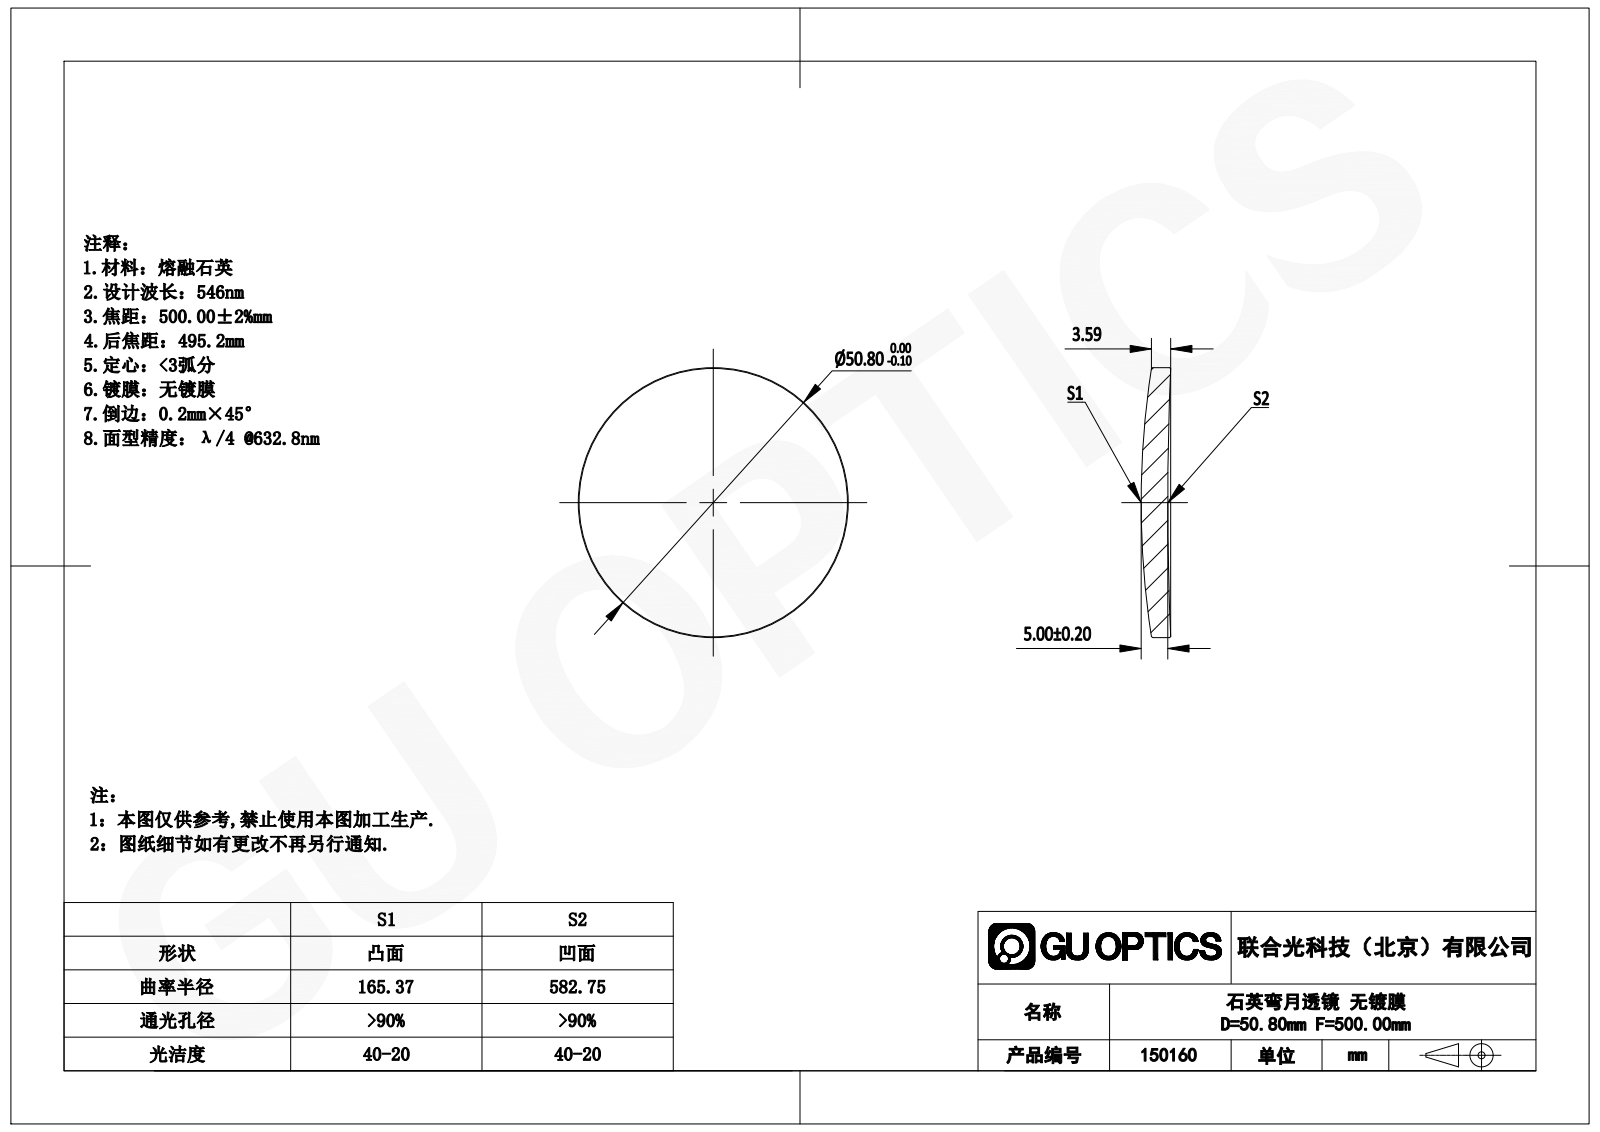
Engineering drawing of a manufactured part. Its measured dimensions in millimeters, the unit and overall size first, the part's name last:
Units: millimetres
Overall size (bounding box): 50.8 × 50.8 × 5.55
Round bosses / shafts (diameter × count): ⌀50.8 ×1
Volume: 8 721 mm³ · Surface area: 4 605 mm²
Bodies: 1 solid, 10 faces (0 planar, 2 cylindrical, 8 other)
Part name (STEP PRODUCT): GLM2-050B-500
STEP written by: SolidWorks 2022 (AUTOMOTIVE_DESIGN)
